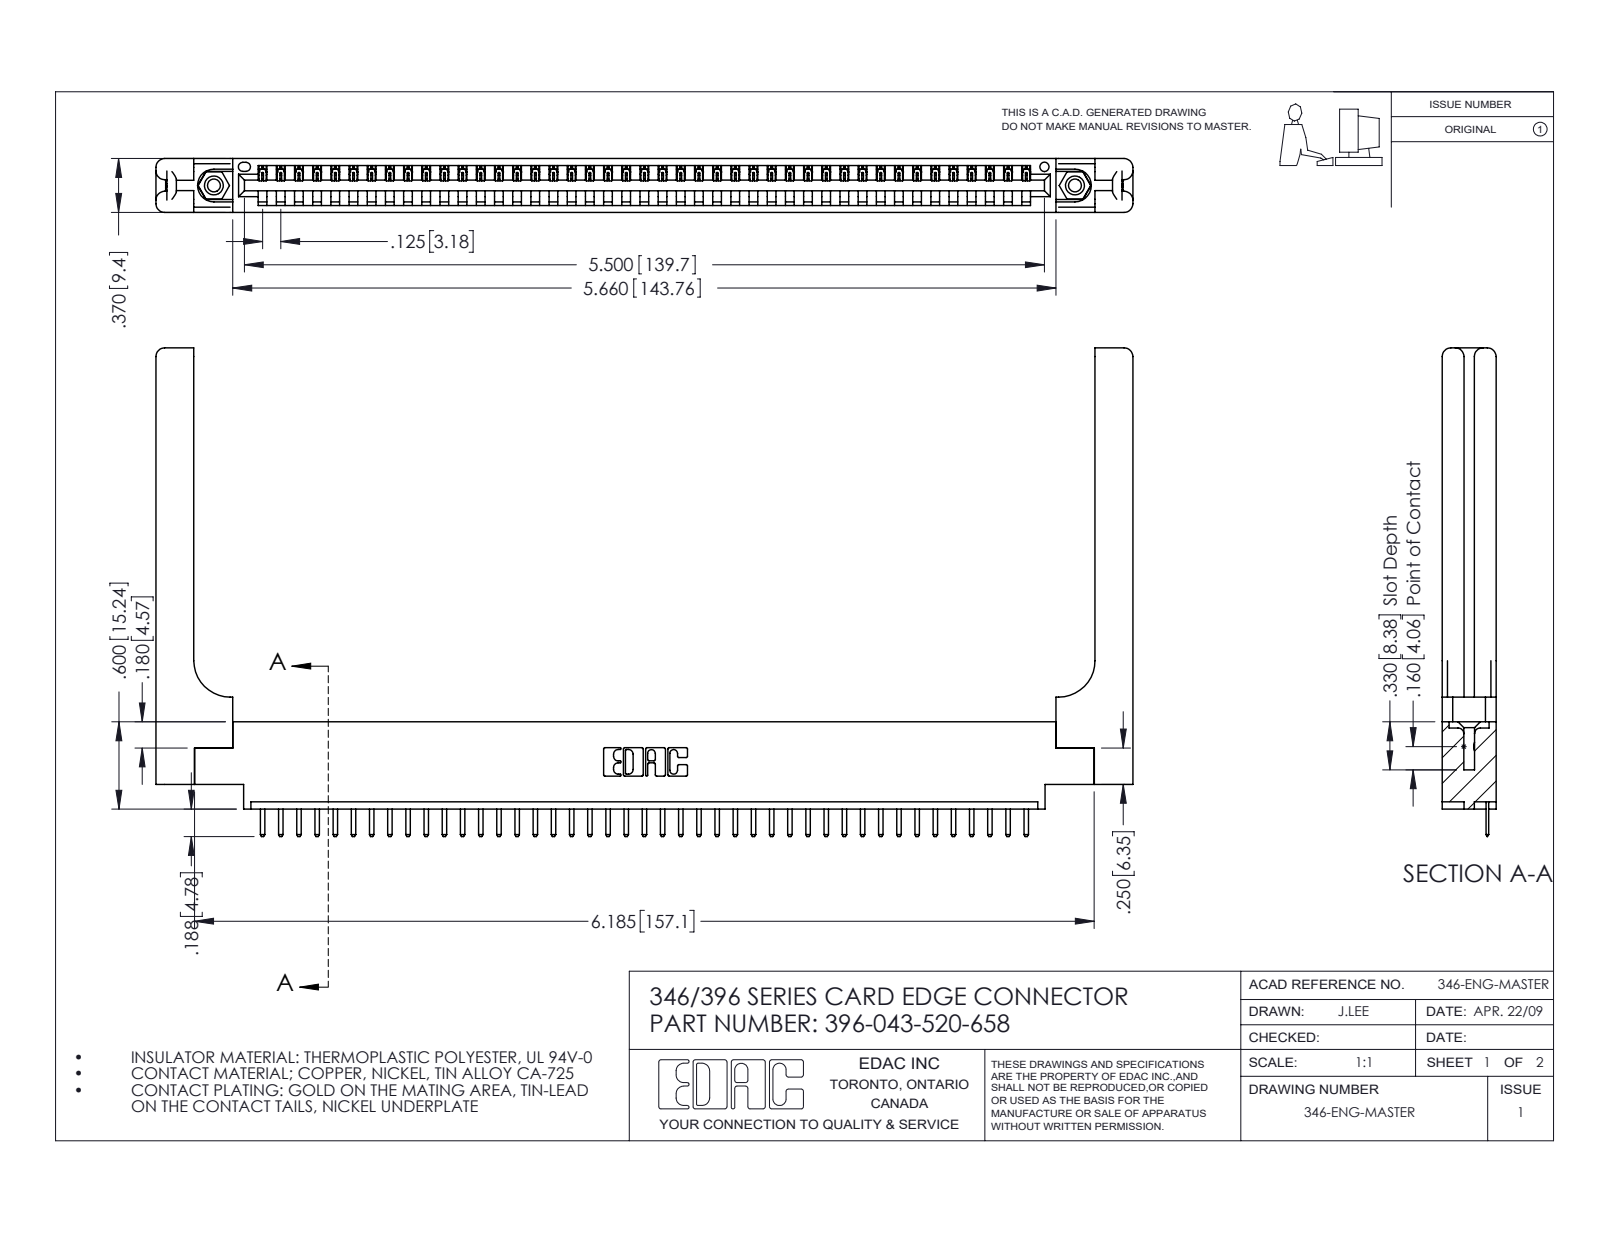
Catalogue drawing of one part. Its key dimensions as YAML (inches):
part_name: "345-292-001_345-293-120; 346 Part_0.170 Offset - 0.156 Dia-TH; 396-043-520-658; 346-220-058_345-220-058 (+1 more)"
step_written_by: "SolidWorks 2016 (CONFIG_CONTROL_DESIGN)"
units: inches
bodies: {solids: 48, faces: 3048, planar: 2034, cylindrical: 954, other: 60}
overall_size: [6.716, 3.358, 0.37]
volume: 1.439
surface_area: 38.75
round_holes:
  - {diameter: 0.089, count: 2}
  - {diameter: 0.125, count: 2}
  - {diameter: 0.156, count: 2}
  - {diameter: 0.064, count: 1}
round_bosses_or_shafts:
  - {diameter: 0.155, count: 2}
partial_cylinders:
  - {radius: 0.01, count: 88}
  - {radius: 0.006, count: 86}
  - {radius: 0.01, count: 22}
  - {radius: 0.06, count: 16}
  - {radius: 0.007, count: 6}
  - {radius: 0.031, count: 6}
  - {radius: 0.026, count: 3}
  - {radius: 0.03, count: 2}
face_to_face_distances: [0.37, 0.048, 0.322, 0.072, 0.148, 0.15, 0.25, 0.298, 0.025, 0.222]
hole_center_spacings: [0.246, 5.711, 5.92]
